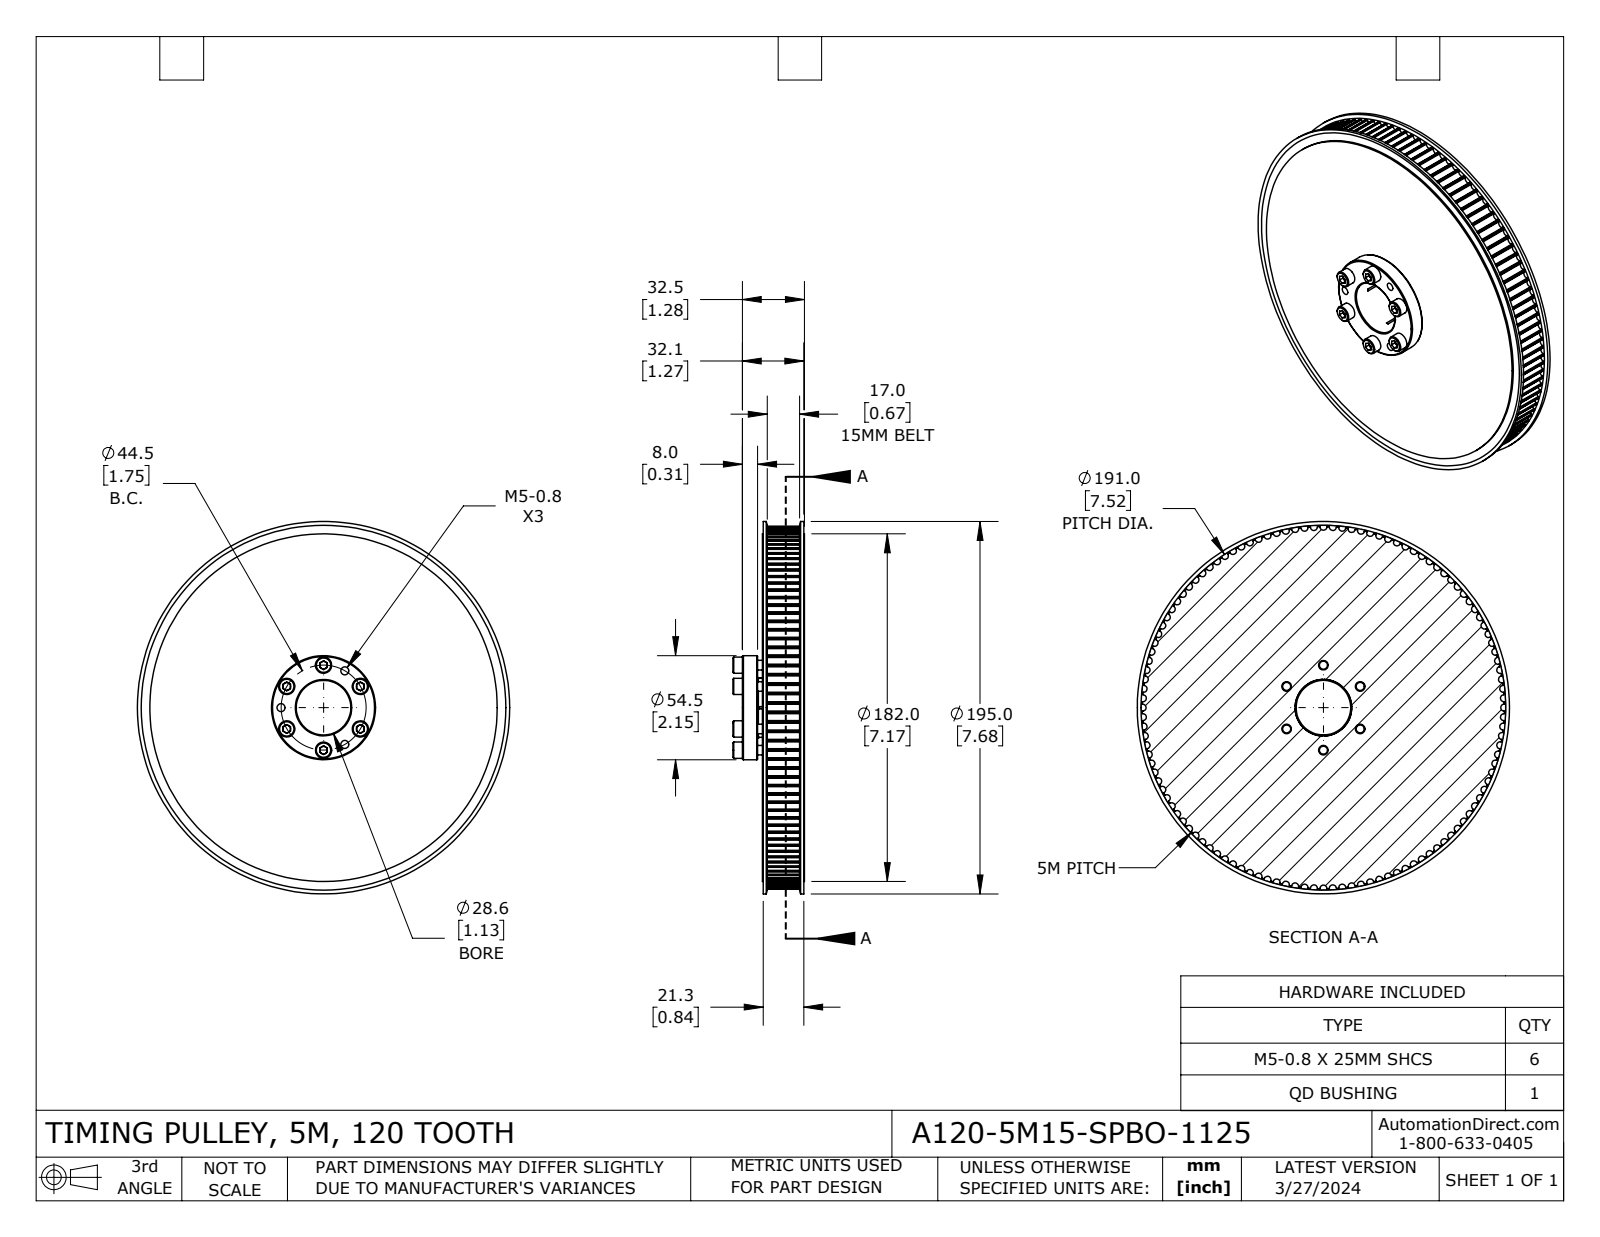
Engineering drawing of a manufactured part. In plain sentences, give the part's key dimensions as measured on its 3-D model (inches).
The part is named "A120-5M15-SPBO-1125". Its 3-D file was written by "SolidWorks 2021 (CONFIG_CONTROL_DESIGN)". It is 10 solids with 849 faces: 116 planar, 671 cylindrical and 62 other. Overall it measures 7.677 by 7.677 by 1.476 inches. Its volume is 37.35 cubic inches and its surface area 166.2 square inches. Round holes: 9 of diameter 0.165, 6 of diameter 0.217, 1 of diameter 1.125, 1 of diameter 1.125, 1 of diameter 1.228, 1 of diameter 7.165. Round bosses or shafts: 6 of diameter 0.335, 6 of diameter 0.197, 1 of diameter 7.677, 1 of diameter 2.146, 1 of diameter 1.227. Partial cylindrical surfaces (rounded edges, fillets, slot ends): 240 of radius 0.012, 120 of radius 0.072, 1 of radius 3.737. The main face-to-face distances are 0.866, 0.098, 0.768, 0.035, 0.831, 0.063, 0.732, 0.669, 0.795, 0.512. The hole center spacings are 0.876, 1.517, 0.454, 1.239, 1.693, 1.517, 0.453, 1.239.
